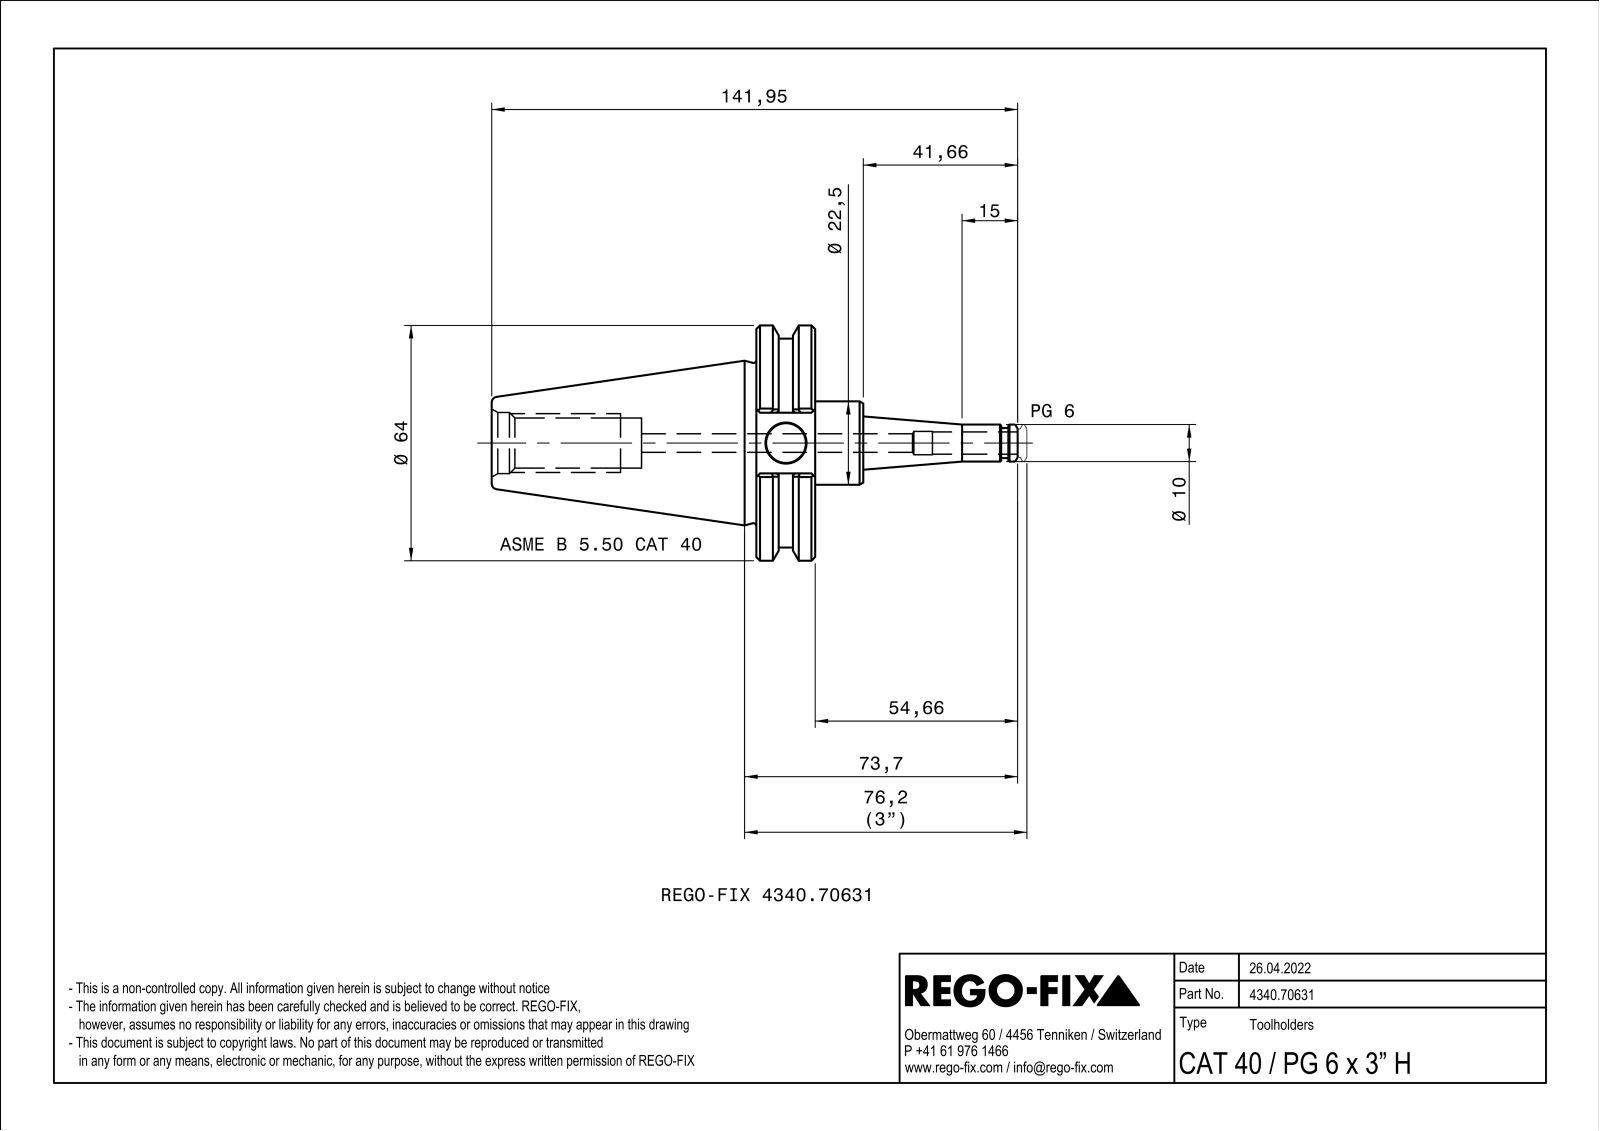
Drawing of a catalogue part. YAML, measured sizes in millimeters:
part_name: "NOCUT"
step_written_by: "SIEMENS PLM Software Solid Edge ST10 (AUTOMOTIVE_DESIGN)"
units: millimeters
bodies: {solids: 1, faces: 98, planar: 34, cylindrical: 20, other: 44}
overall_size: [141.95, 63.5, 60.79]
volume: 113534
surface_area: 22381
round_holes:
  - {diameter: 5, count: 1}
  - {diameter: 6.3, count: 1}
  - {diameter: 10.7, count: 1}
  - {diameter: 13.53, count: 1}
  - {diameter: 16.5, count: 1}
round_bosses_or_shafts:
  - {diameter: 63.5, count: 1}
  - {diameter: 56.36, count: 1}
  - {diameter: 22.5, count: 1}
  - {diameter: 10, count: 1}
  - {diameter: 8.1, count: 1}
partial_cylinders:
  - {radius: 0.5, count: 4}
face_to_face_distances: [15.87, 47.33, 13, 28.87, 16.38, 100.29, 87.29, 71.42, 18.99, 5.99]
